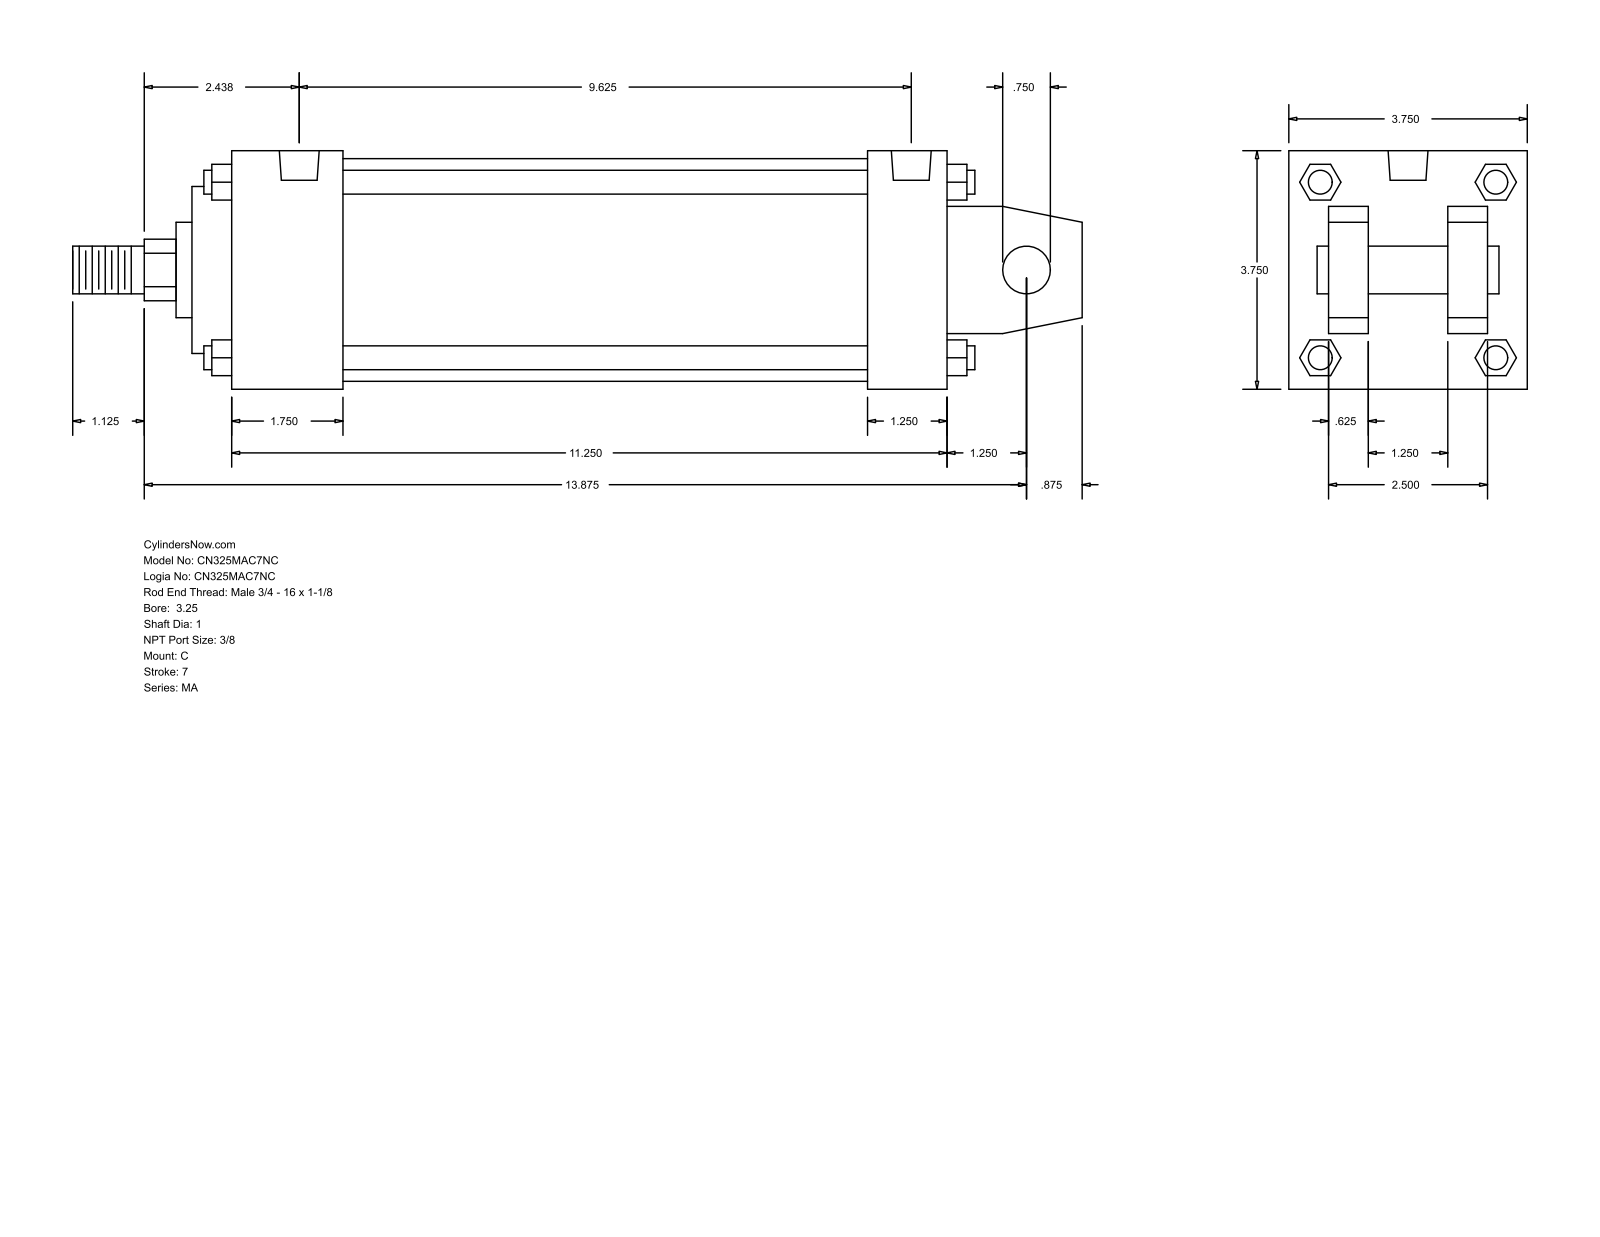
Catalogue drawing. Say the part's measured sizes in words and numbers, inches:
The part is named "MA_C__0325_1". Its 3-D file was written by "GSSL Pune (CONFIG_CONTROL_DESIGN)". It is 0 solids with 141 faces: 109 planar, 32 cylindrical and 0 other. Overall it measures 15.875 by 3.75 by 3.75 inches. Round holes: 4 of diameter 0.437, 2 of diameter 0.627. Round bosses or shafts: 4 of diameter 0.375, 2 of diameter 0.75, 1 of diameter 3.5, 1 of diameter 2.625, 1 of diameter 1.5, 1 of diameter 1. Partial cylindrical surfaces (rounded edges, fillets, slot ends): 1 of radius 0.484. The main face-to-face distances are 3.75, 0.625, 2.5, 11.25, 1.25, 3.125, 1.875, 10, 1.25, 1.75. The hole center spacings are 9.25, 0.187, 0.188, 9.437, 9.438, 9.625.
